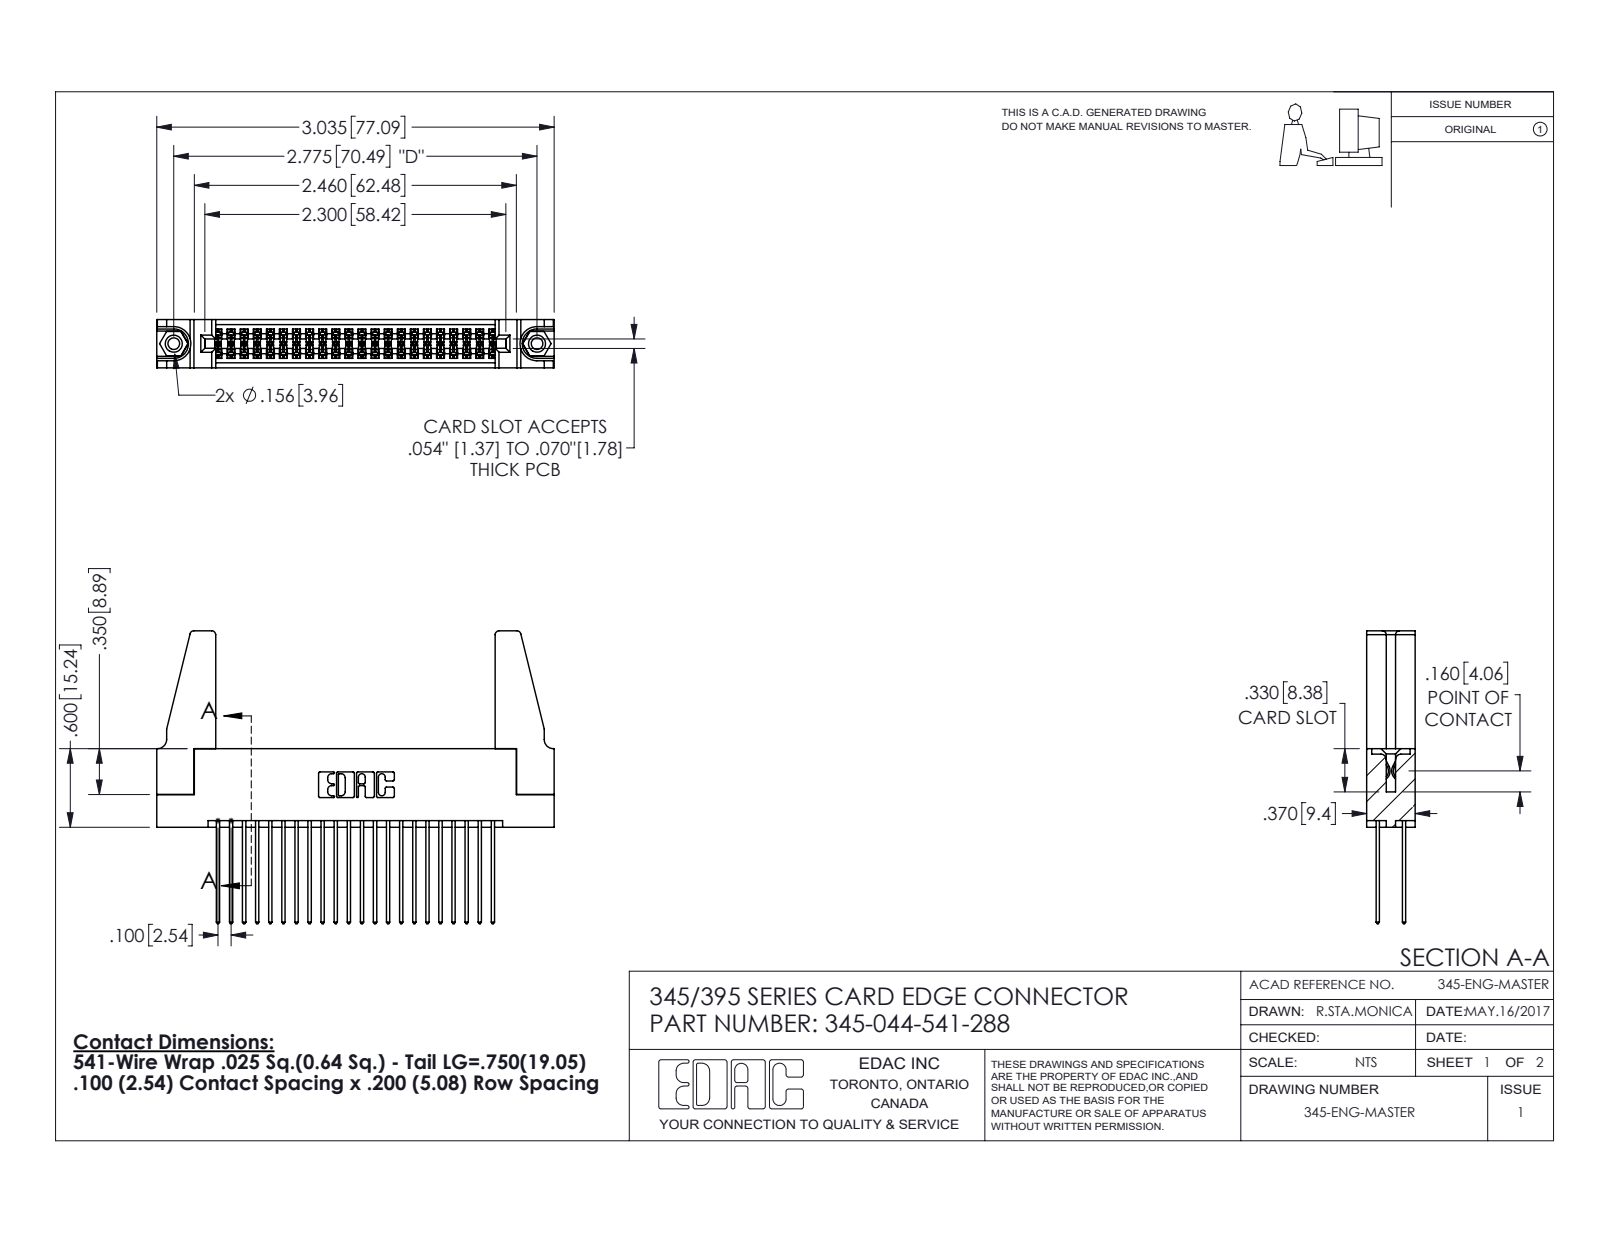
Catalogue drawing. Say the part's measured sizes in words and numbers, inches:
The part is named "345-250-001_345-250-001-102; 345 Part_Flush Mounting Lugs - 0.156 Dia-TH; 345-220-078_345-220-088; 345-292-001_345-293-141 (+1 more)". Its 3-D file was written by "SolidWorks 2016 (CONFIG_CONTROL_DESIGN)". It is 49 solids with 2450 faces: 1604 planar, 830 cylindrical and 16 other. Overall it measures 3.036 by 2.237 by 0.37 inches. Its volume is 0.66 cubic inches and its surface area 23.39 square inches. Round holes: 2 of diameter 0.089, 2 of diameter 0.125, 2 of diameter 0.156, 1 of diameter 0.064. Round bosses or shafts: 2 of diameter 0.155. Partial cylindrical surfaces (rounded edges, fillets, slot ends): 66 of radius 0.006, 44 of radius 0.01, 22 of radius 0.01, 8 of radius 0.03, 6 of radius 0.007, 6 of radius 0.031, 3 of radius 0.026, 2 of radius 0.014. The main face-to-face distances are 0.072, 0.298, 0.2, 0.37, 0.098, 0.272, 0.025, 0.225, 0.175, 0.149. The hole center spacings are 0.27, 2.541, 2.775.
